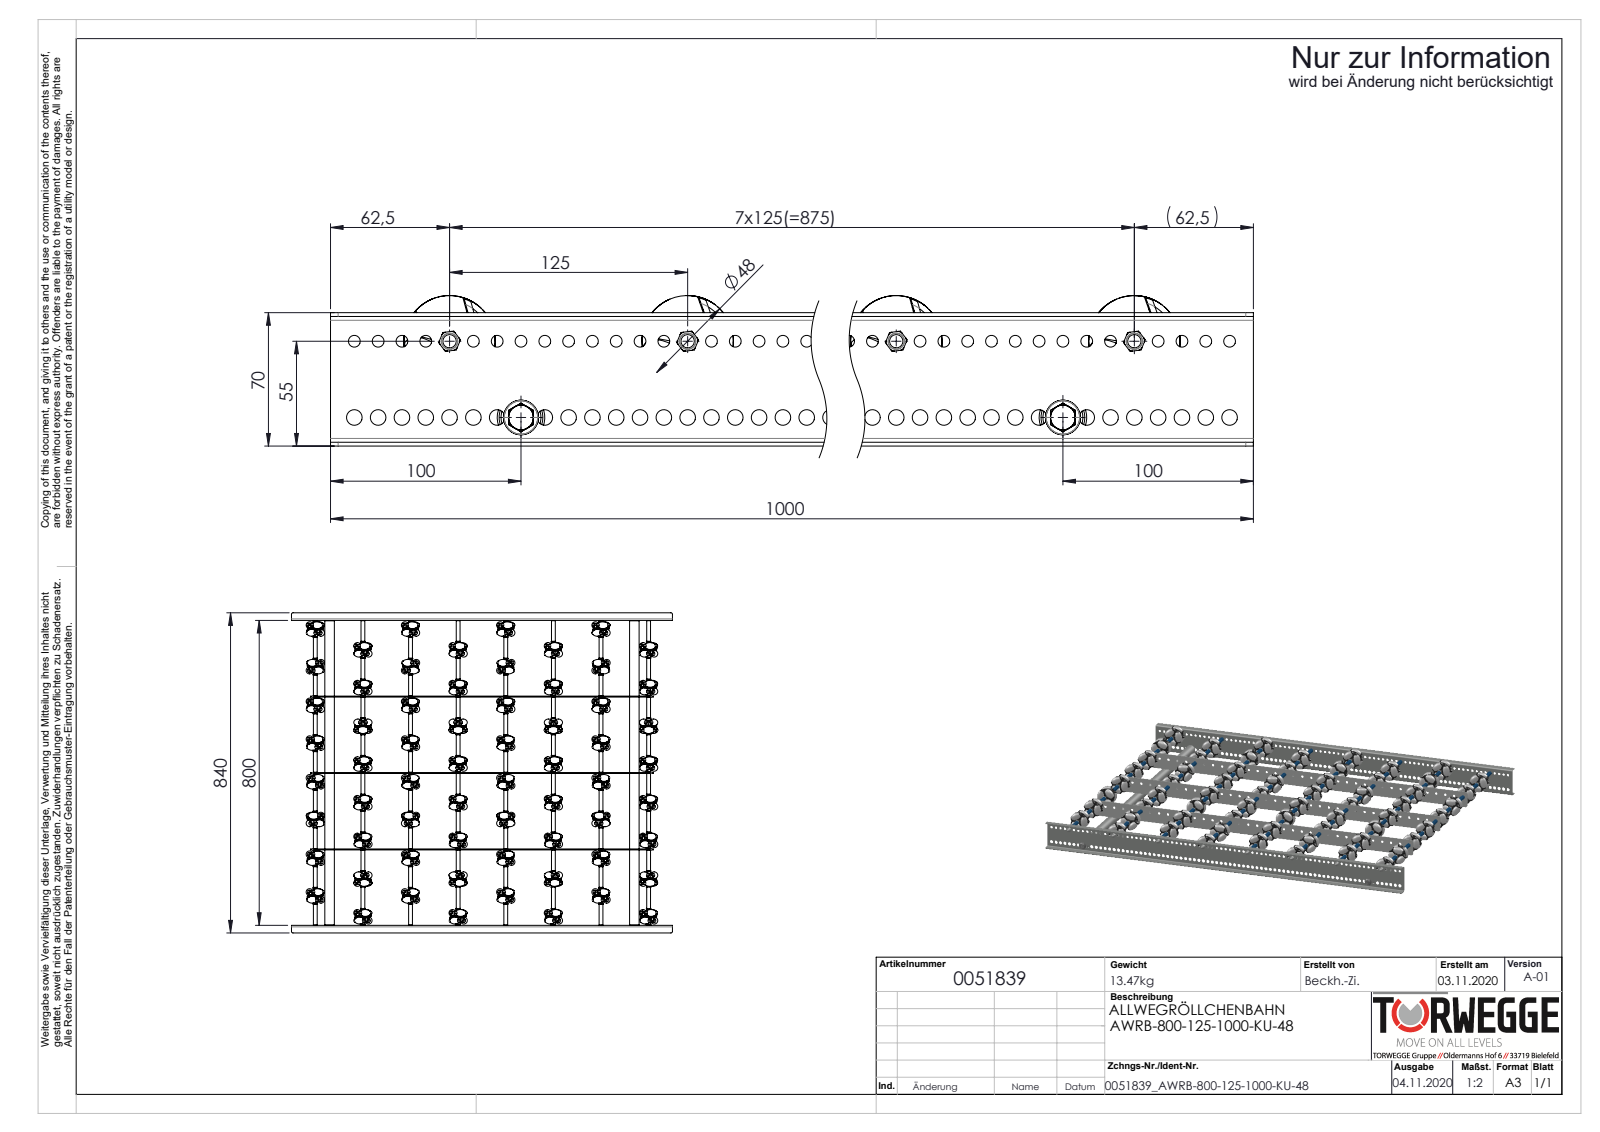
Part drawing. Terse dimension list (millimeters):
name: 0027528_BUCHSE-HOHLNIETE ZU AWR48; AWR48_Halter; 0019719_Gewindestange-M6_L=820; S100994_Sperrzahnschraube_M08x16-8.8-A2K (+8 more)
written by: SolidWorks 2020 (AUTOMOTIVE_DESIGN)
unit: mm
bodies: 1063 solids, 19094 faces (6554 planar, 7652 cylindrical, 4888 other)
size: 1000 × 840 × 79
volume: 3 984 000 mm³; area: 2 821 000 mm²
holes: 384× ⌀3.7, 384× ⌀4.2, 79× ⌀6.2, 79× ⌀8.2, 36× ⌀6.5, 8× ⌀4.92, 8× ⌀8.4, 2× ⌀6.8, 2× ⌀21
bosses: 384× ⌀4, 322× ⌀3.7, 10× ⌀8, 8× ⌀47.1, 8× ⌀42, 8× ⌀11, 8× ⌀10, 8× ⌀7
rounds: 8× R4, 4× R2, 4× R5
face distances: 2, 200.5, 802, 2.5, 401, 203, 198, 68, 800, 804
hole spacings: 36.06, 36.05, 99, 36.07, 122.72, 36.04, 125, 250
